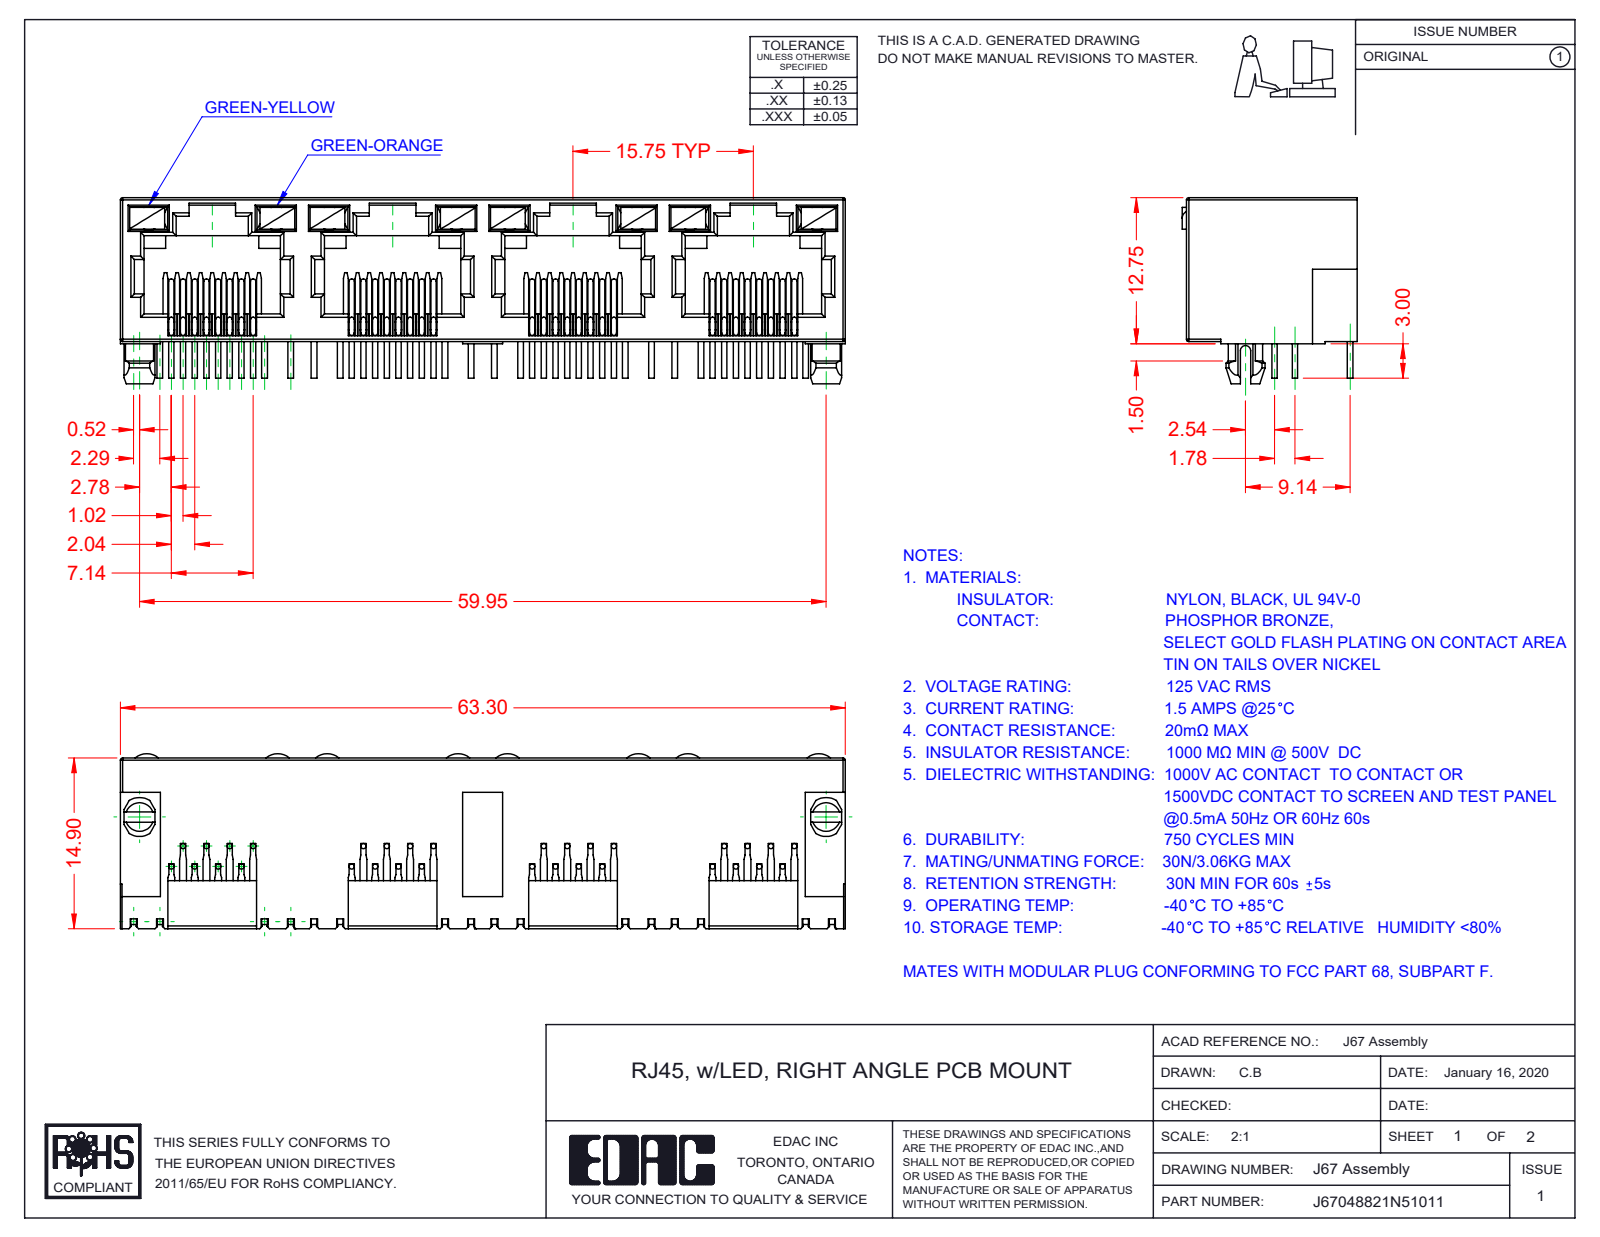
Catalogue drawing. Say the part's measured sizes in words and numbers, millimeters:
The part is named "67 Insulator; 67 LED LH_5-Green-Yellow; 67 Contacts; J67048822N57011 (+1 more)". Its 3-D file was written by "SolidWorks 2016 (CONFIG_CONTROL_DESIGN)". It is 41 solids with 2481 faces: 1781 planar, 492 cylindrical and 208 other. Overall it measures 63.3 by 16.25 by 15.28 millimeters. Its volume is 5 159 cubic millimeters and its surface area 11 573 square millimeters. Round bosses or shafts: 96 of diameter 0.46. Partial cylindrical surfaces (rounded edges, fillets, slot ends): 66 of radius 0.2, 29 of radius 0.3, 9 of radius 0.45, 8 of radius 1.55, 2 of radius 1.5, 2 of radius 1.7, 1 of radius 0.35, 1 of radius 1. The main face-to-face distances are 0.5, 12.55, 1.89, 0.89, 10, 15.75, 1, 1.39, 11, 11.89.
